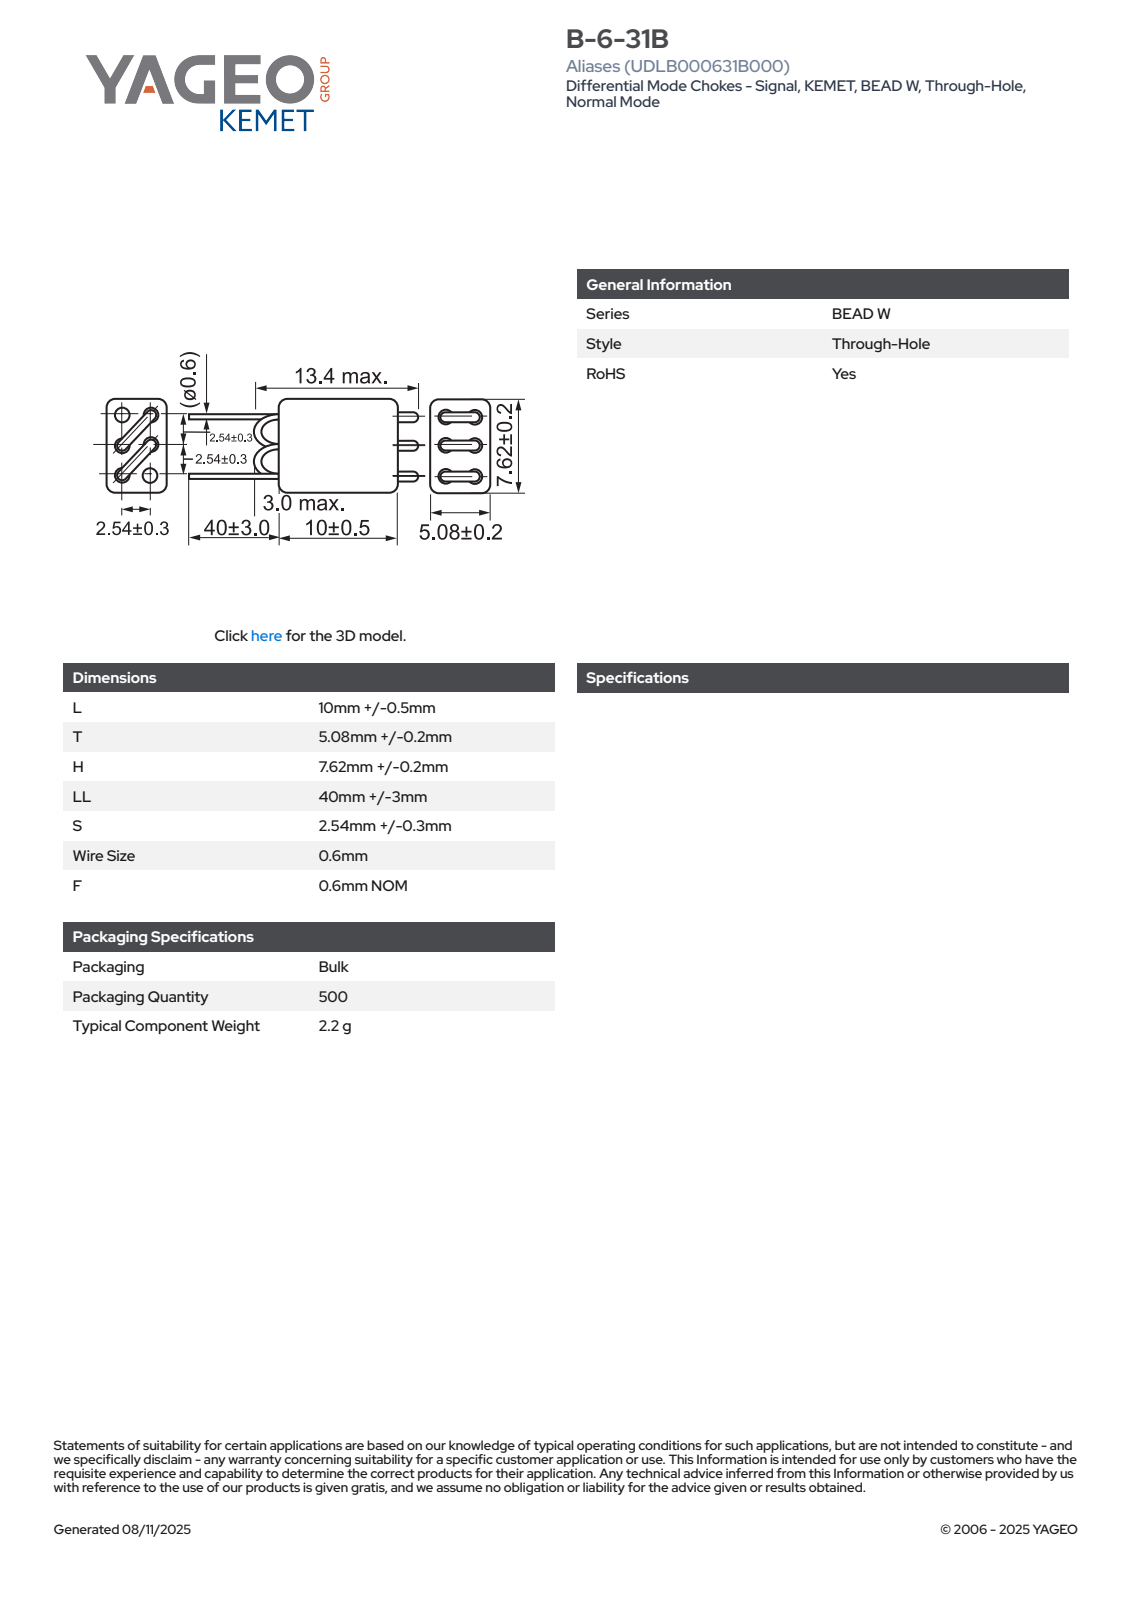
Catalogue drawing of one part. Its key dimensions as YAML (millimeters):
part_name: "IL_B631B_L10.5T5.28H7.82S2.54LL43G3"
step_written_by: "SolidWorks 2014 (AUTOMOTIVE_DESIGN)"
units: millimeters
bodies: {solids: 1, faces: 139, planar: 77, cylindrical: 40, other: 22}
overall_size: [54.78, 7.82, 5.29]
volume: 461
surface_area: 547
round_holes:
  - {diameter: 0.9, count: 6}
round_bosses_or_shafts:
  - {diameter: 0.6, count: 2}
partial_cylinders:
  - {radius: 0.3, count: 12}
face_to_face_distances: [5.28, 7.82, 10.5, 5.29, 10.4, 10.3, 53.5, 53.4, 43.1, 43]
hole_center_spacings: [2.54, 3.59, 5.08, 5.68]
